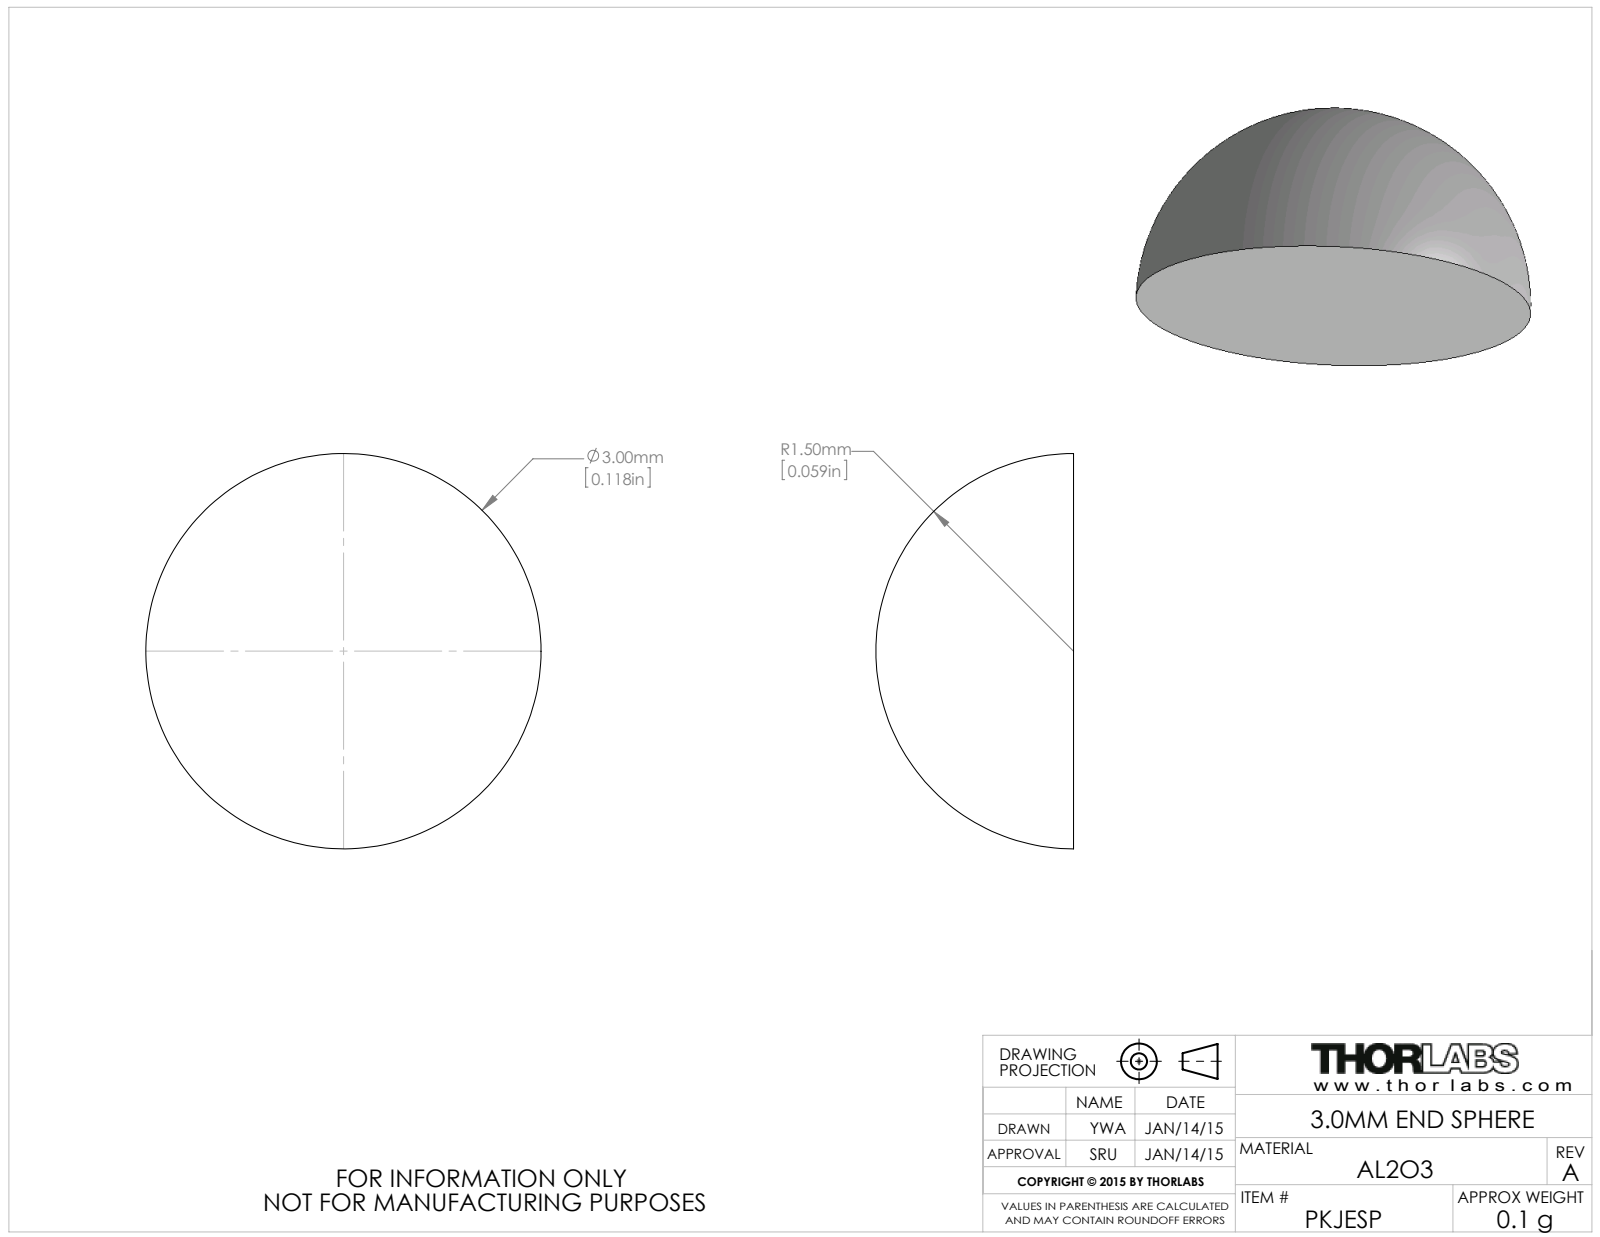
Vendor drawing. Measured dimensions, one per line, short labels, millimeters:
name: PKJESP
written by: SolidWorks 2012 (AUTOMOTIVE_DESIGN)
unit: mm
bodies: 1 solid, 3 faces (1 planar, 0 cylindrical, 2 other)
size: 3 × 3 × 1.5
volume: 7 mm³; area: 21 mm²
